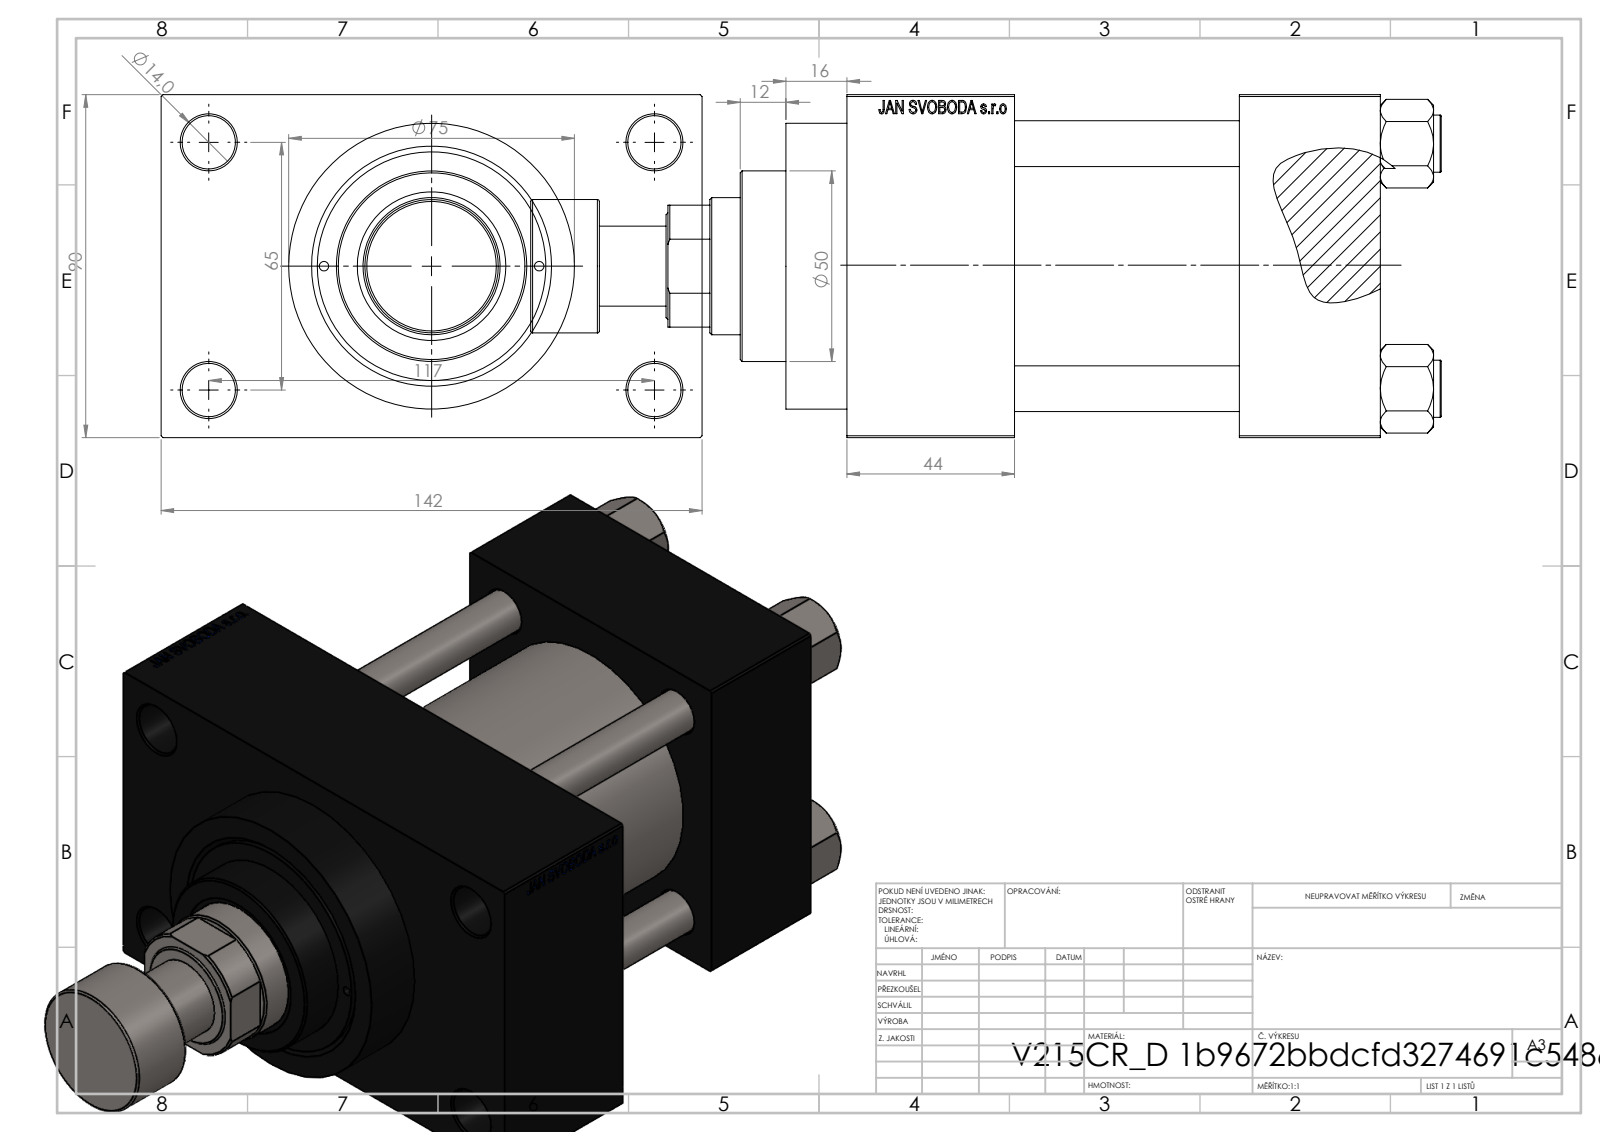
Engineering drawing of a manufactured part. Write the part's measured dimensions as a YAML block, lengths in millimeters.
part_name: "NUT_M5_D; V215CR_ROD_END_F; V215CR_D_TYCINKA; V215CR_D_Body (+2 more)"
step_written_by: "SolidWorks 2019 (CONFIG_CONTROL_DESIGN)"
units: millimeters
bodies: {solids: 12, faces: 1125, planar: 503, cylindrical: 96, other: 526}
overall_size: [239, 142, 90]
volume: 1135000
surface_area: 211267
round_holes:
  - {diameter: 12, count: 4}
  - {diameter: 14, count: 4}
  - {diameter: 2.5, count: 2}
  - {diameter: 7, count: 2}
  - {diameter: 20.96, count: 2}
  - {diameter: 30, count: 2}
  - {diameter: 25.5, count: 1}
  - {diameter: 36, count: 1}
  - {diameter: 39, count: 1}
  - {diameter: 50, count: 1}
  - {diameter: 60, count: 1}
  - {diameter: 63, count: 1}
round_bosses_or_shafts:
  - {diameter: 15, count: 4}
  - {diameter: 75, count: 1}
  - {diameter: 69, count: 1}
  - {diameter: 35, count: 1}
  - {diameter: 21, count: 1}
face_to_face_distances: [90, 59, 37, 96, 140, 103, 44, 26, 116, 142]
hole_center_spacings: [26.35, 32.39, 44.4, 45.47, 64.3, 66.92, 68.42, 69.81]
